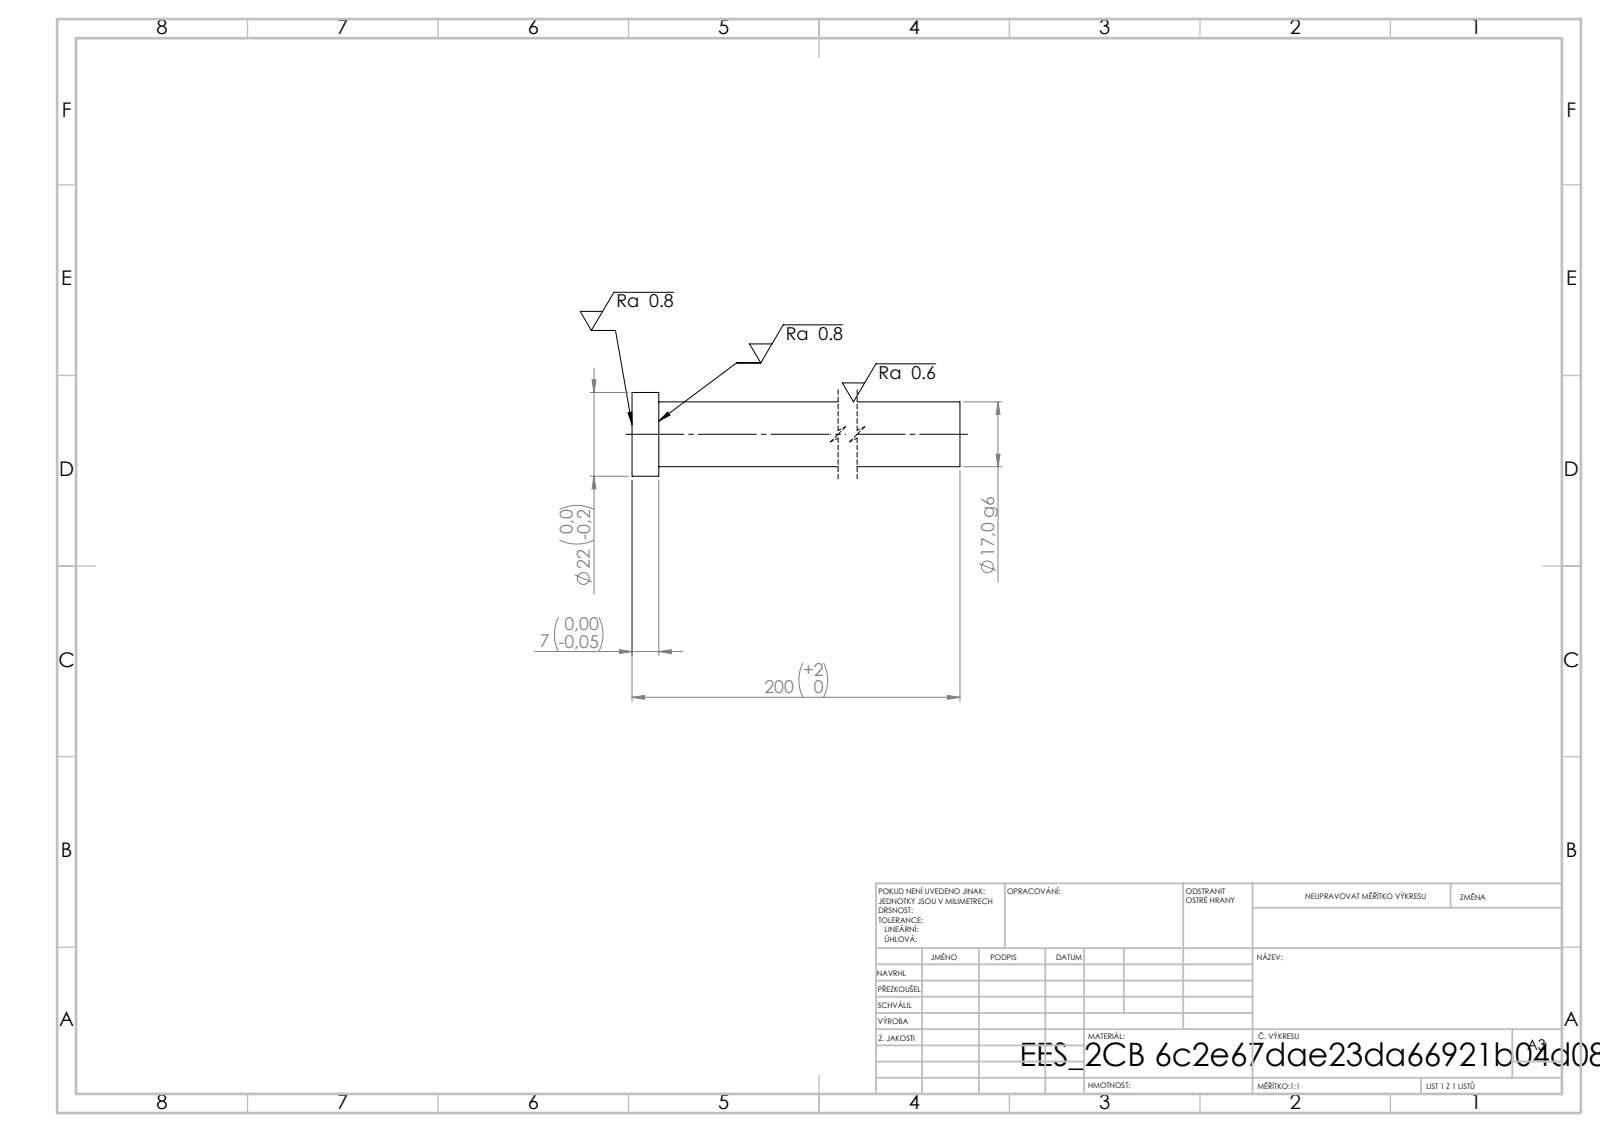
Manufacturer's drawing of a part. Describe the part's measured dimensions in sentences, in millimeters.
Its 3-D file was written by "SolidWorks 2019 (CONFIG_CONTROL_DESIGN)". It is 1 solid with 7 faces: 3 planar, 4 cylindrical and 0 other. Overall it measures 200 by 22 by 22 millimeters. Its volume is 46 468 cubic millimeters and its surface area 11 552 square millimeters. Round bosses or shafts: 1 of diameter 22, 1 of diameter 17. The main face-to-face distances are 200, 7, 193.
